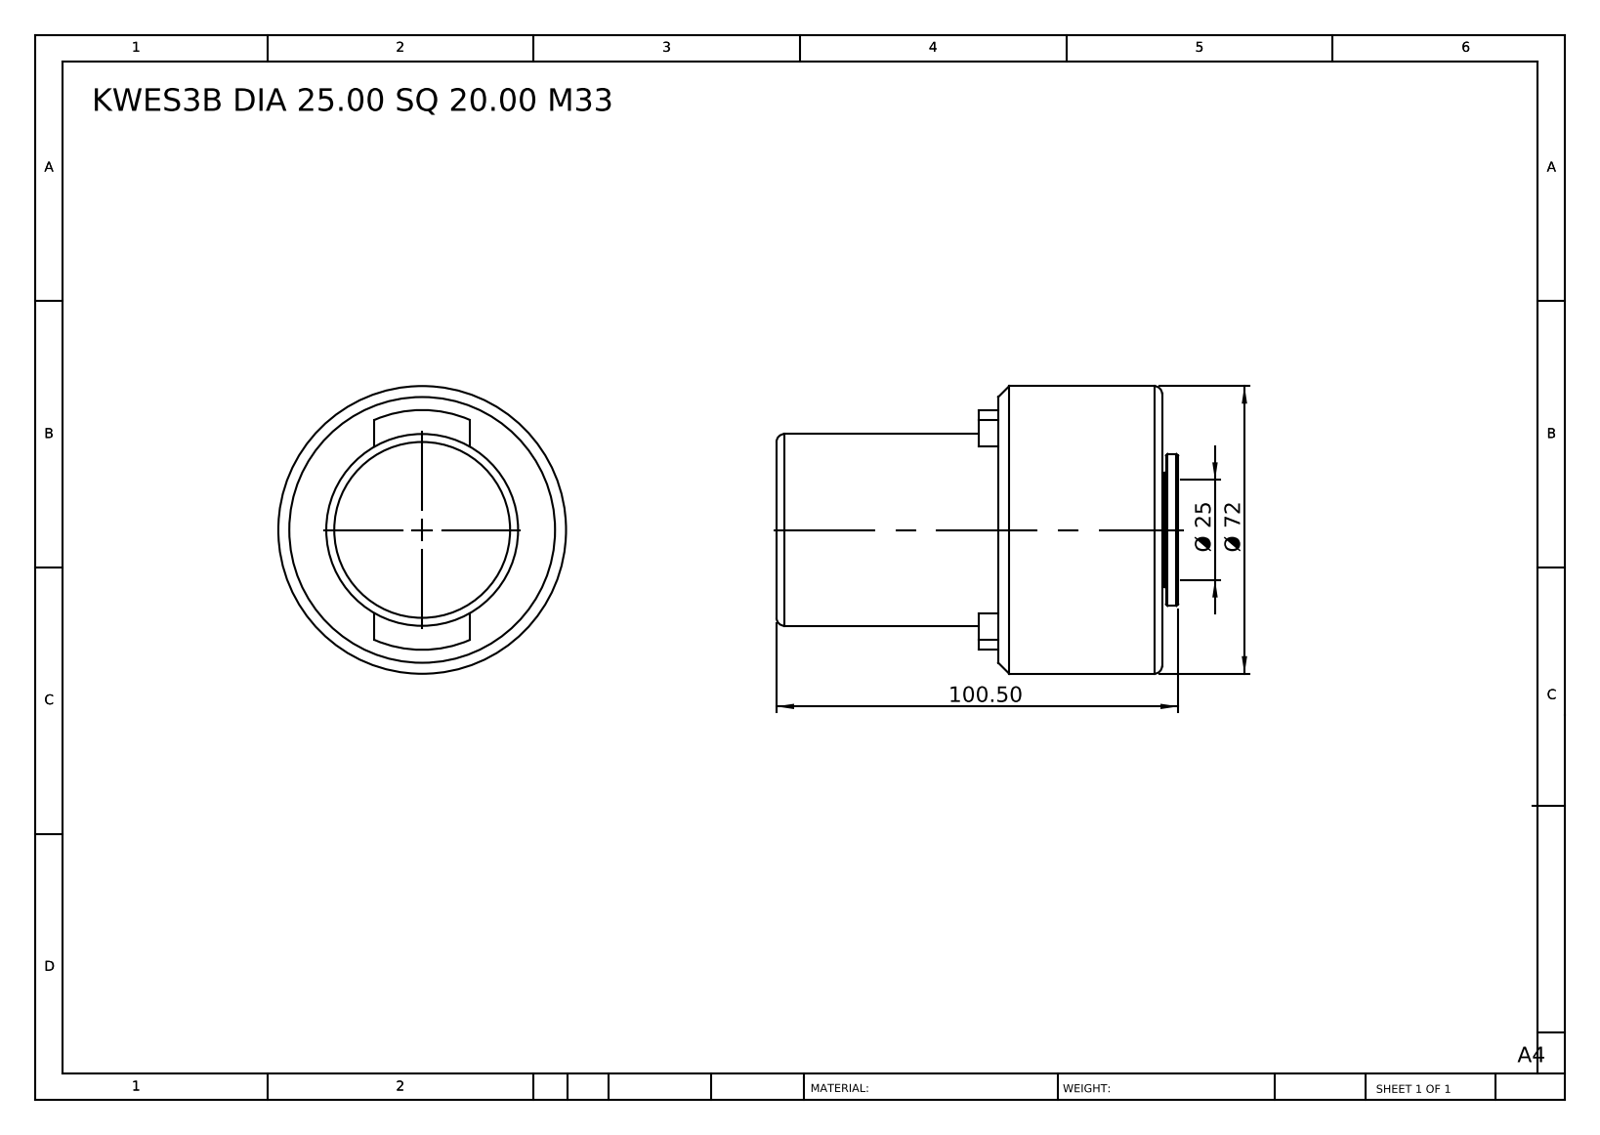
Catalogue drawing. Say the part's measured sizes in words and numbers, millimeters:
The part is named "KWES3B DIA 25.00 SQ 20.00 1'''''''' G(BSP)". Its 3-D file was written by "SolidWorks 2014 (CONFIG_CONTROL_DESIGN)". It is 1 solid with 39 faces: 12 planar, 13 cylindrical and 14 other. Overall it measures 100.5 by 72 by 72 millimeters. Its volume is 252 077 cubic millimeters and its surface area 29 702 square millimeters. Round holes: 1 of diameter 25. Round bosses or shafts: 1 of diameter 72, 1 of diameter 48, 1 of diameter 38, 1 of diameter 28.5. Partial cylindrical surfaces (rounded edges, fillets, slot ends): 1 of radius 30. The main face-to-face distances are 96.5, 55.5, 41, 5, 100.5, 45, 4, 60.5, 36, 40.
